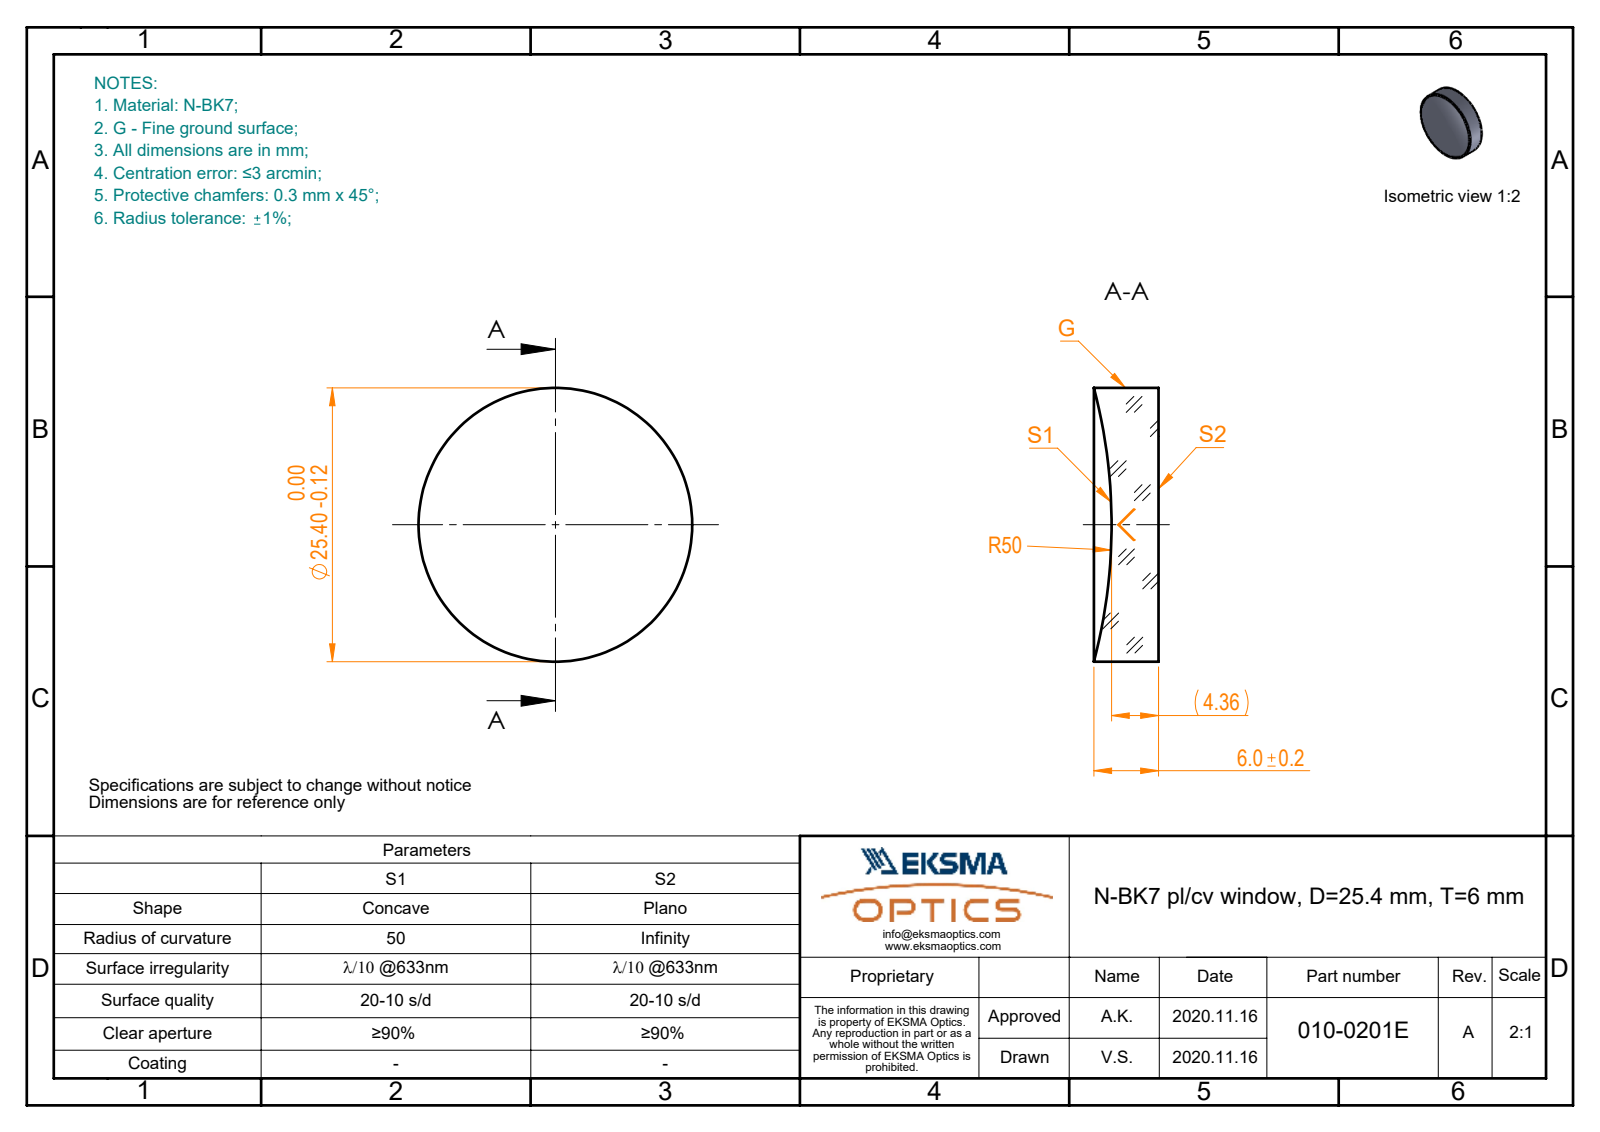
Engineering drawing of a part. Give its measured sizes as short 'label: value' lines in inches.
name: 010-0201E_N-BK7_PCV_mirror
written by: SolidWorks 2019 (CONFIG_CONTROL_DESIGN)
unit: in
bodies: 1 solid, 5 faces (1 planar, 2 cylindrical, 2 other)
size: 1 × 1 × 0.236
volume: 0.16 in³; area: 2.327 in²
bosses: 1× ⌀1
